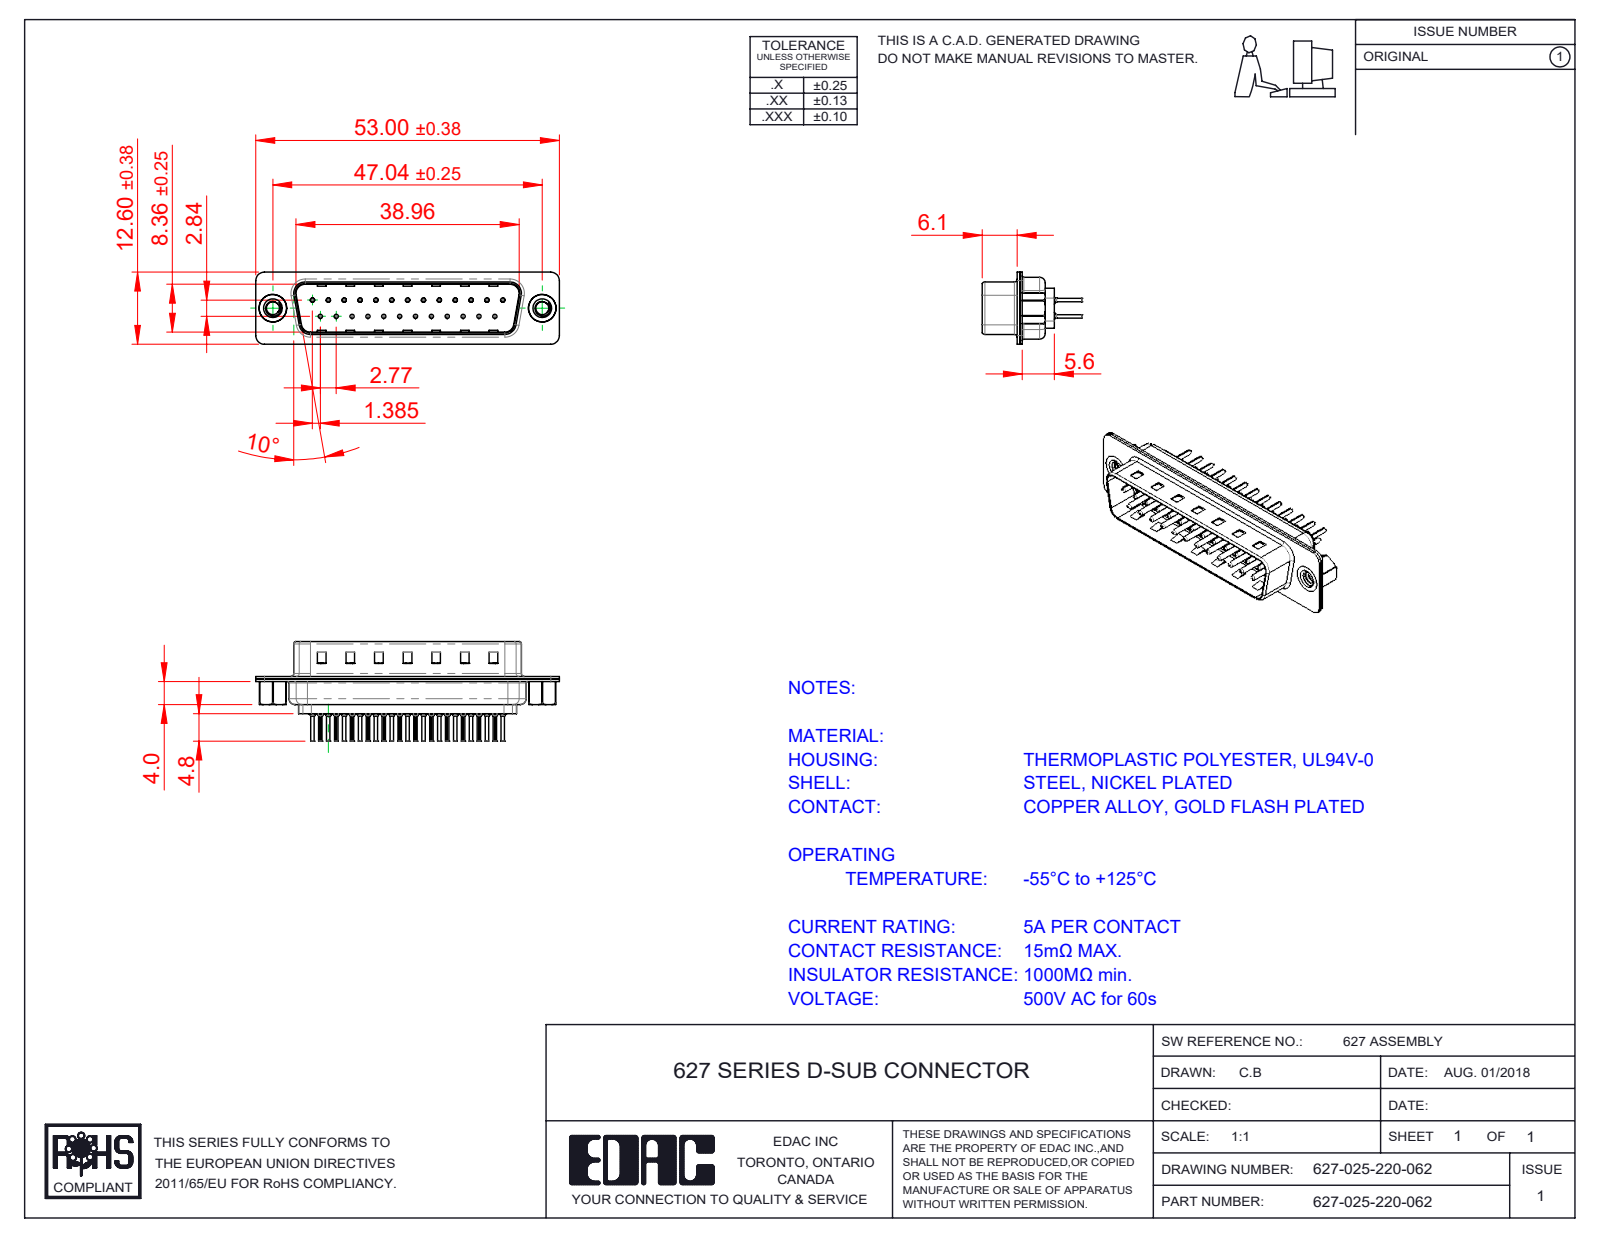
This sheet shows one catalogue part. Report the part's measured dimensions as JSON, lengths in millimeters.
{"part_name": "627 Shell Front_25 Contacts; 627 Shell Rear_25 Contacts; 627 4-40 Threaded Rivet; 627 Housing_25 LP (+3 more)", "step_written_by": "SolidWorks 2020 (CONFIG_CONTROL_DESIGN)", "units": "millimeters", "bodies": {"solids": 30, "faces": 2822, "planar": 771, "cylindrical": 1060, "other": 991}, "overall_size": [53, 17.3, 12.6], "volume_mm3": 2677, "surface_area_mm2": 7794, "round_holes": [[0.2, 25], [0.35, 25], [1.1, 25], [1.6, 25], [2.26, 2], [4, 2], [4.8, 2]], "round_bosses_or_shafts": [[2, 25], [1.5, 25], [0.75, 25], [0.6, 25], [5, 2], [4.9, 2]], "partial_cylinders_radius": [[0.1, 50], [1.5, 16], [2, 12], [0.5, 8], [1.6, 8], [0.25, 4], [0.6, 4], [0.65, 4]], "face_to_face_distances": [0.4, 0.45, 0.82, 9.58, 8.76, 0.9, 1.5, 1.4, 6.5, 6.05], "hole_center_spacings": [3.16, 8.31, 2.77, 5.54, 11.08, 16.62, 5.03, 5.04]}
